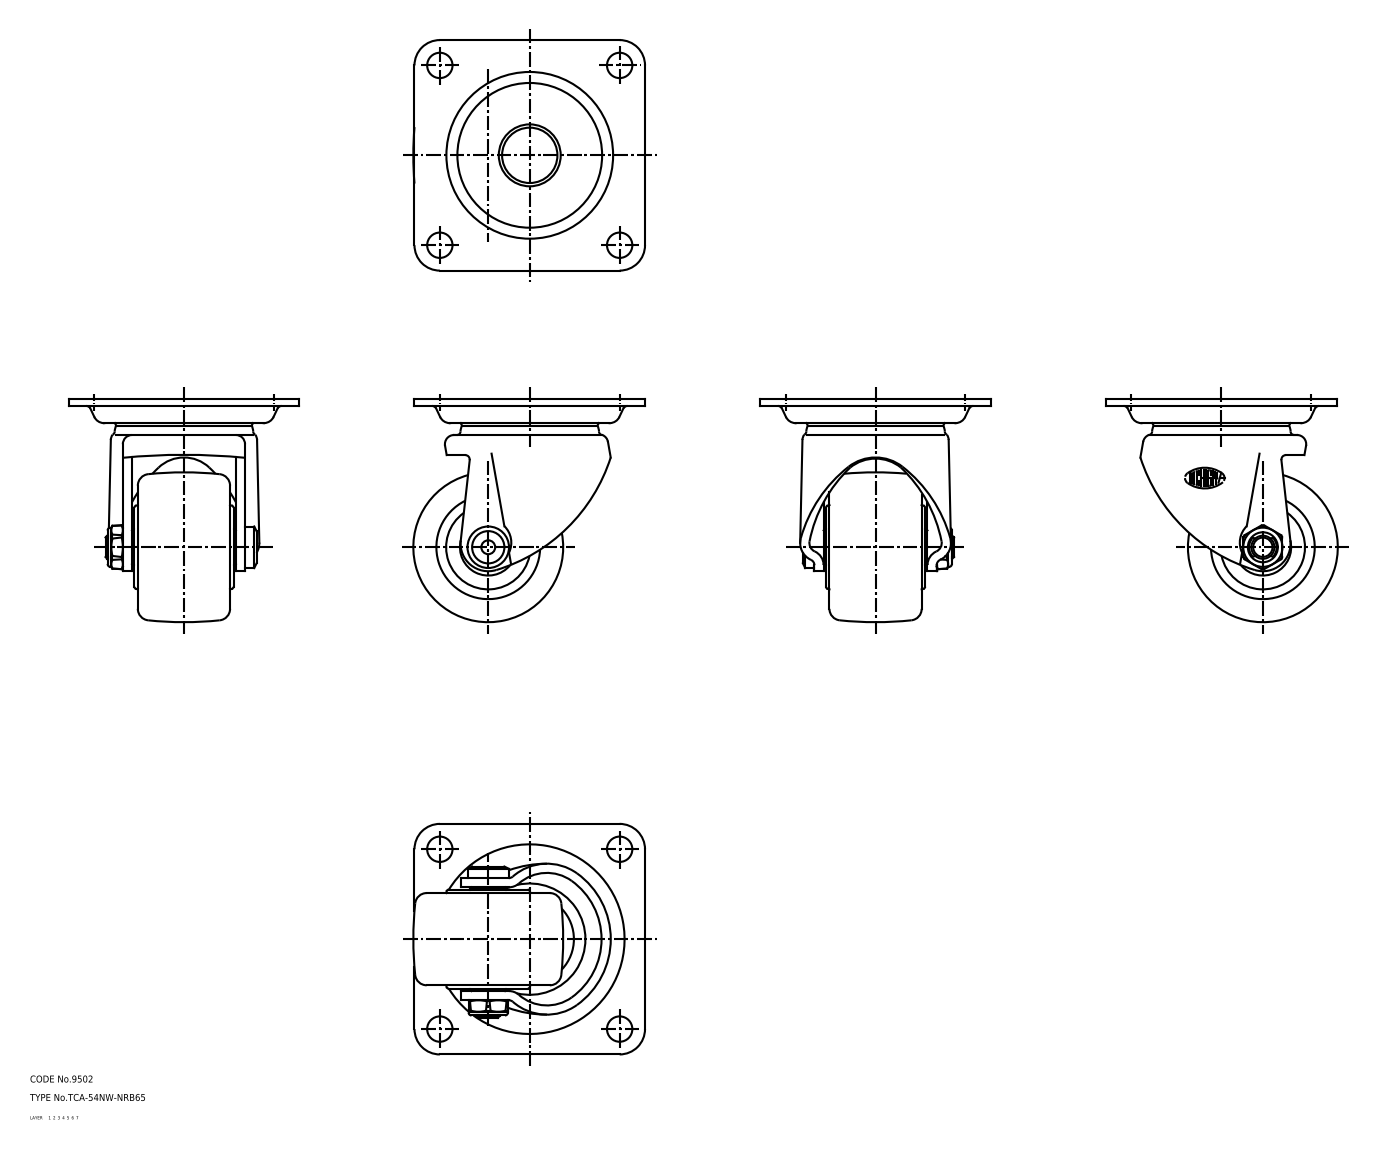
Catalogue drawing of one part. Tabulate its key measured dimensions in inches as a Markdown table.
| quantity | value |
| --- | --- |
| part name | wheel; seal; nut; mounting plate (+3 more) |
| STEP written by | CADfix (AUTOMOTIVE_DESIGN) |
| units | inches |
| bodies | 7 solids, 233 faces (0 planar, 0 cylindrical, 233 other) |
| overall size | 3.957 × 3.937 × 3.819 |
| volume | 14.61 in³ |
| surface area | 112.7 in² |
